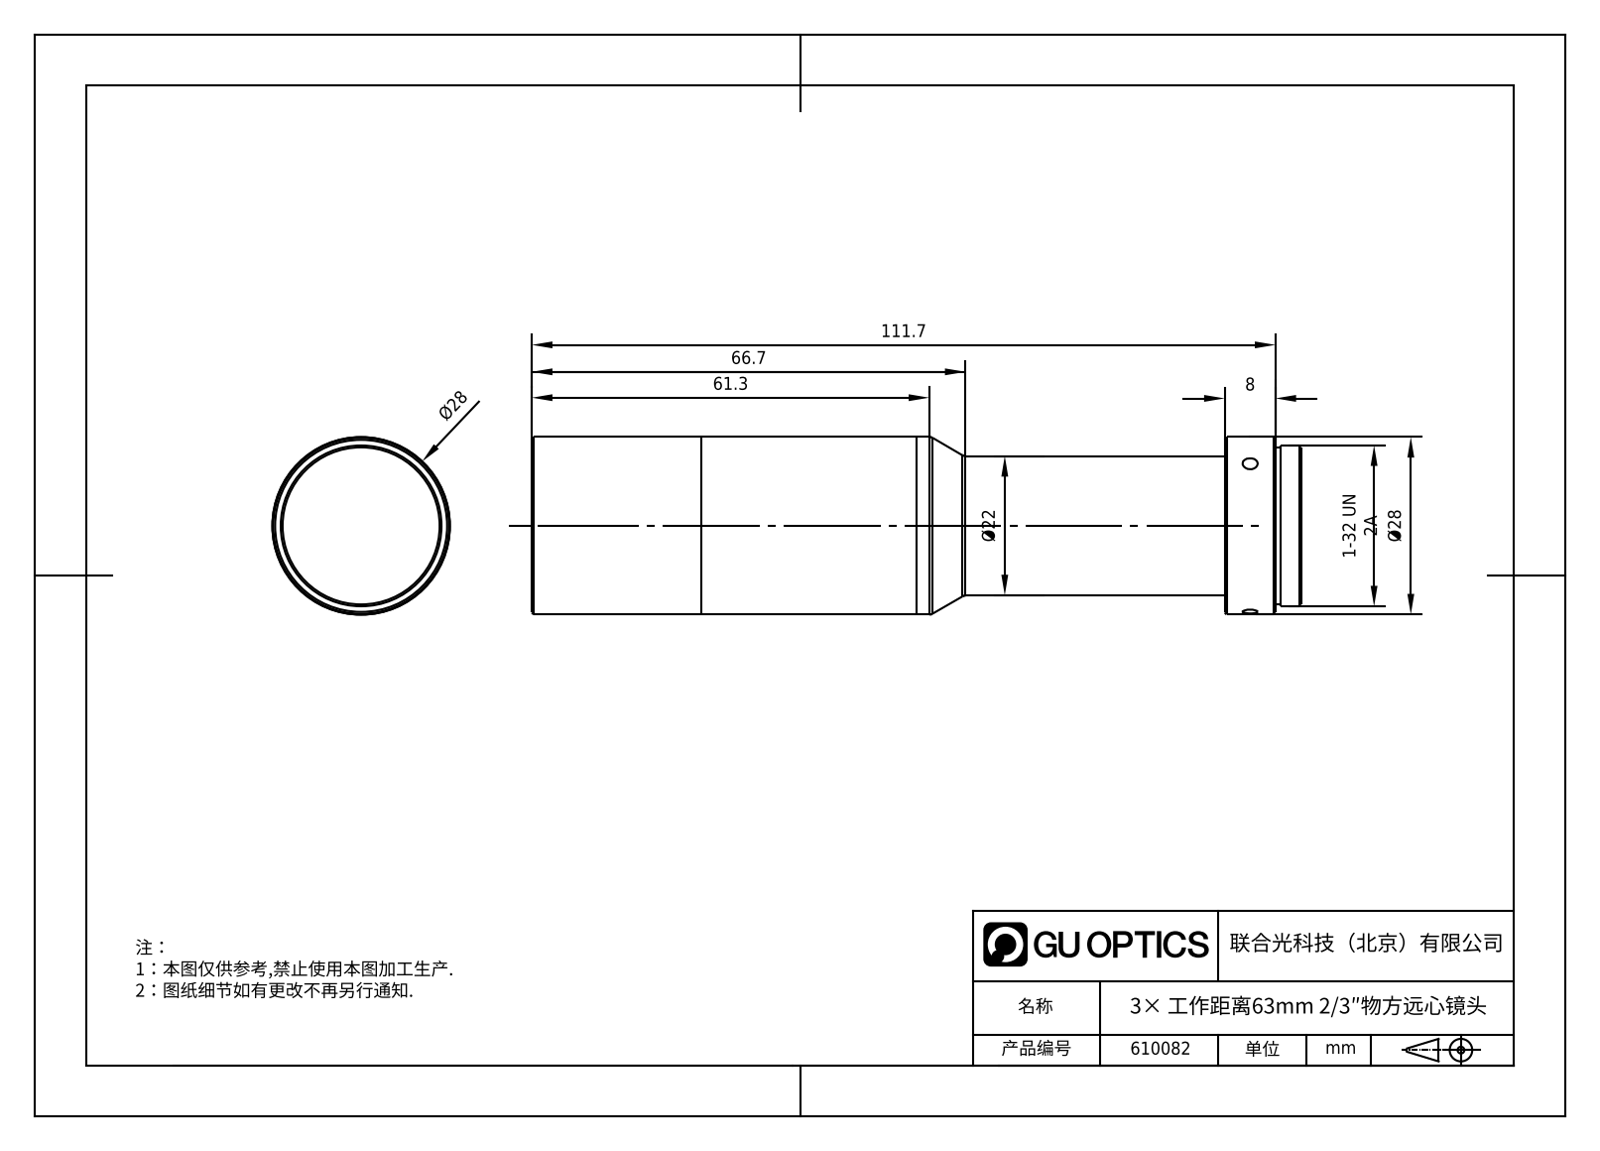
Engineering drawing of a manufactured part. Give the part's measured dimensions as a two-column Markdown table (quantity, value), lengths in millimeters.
| quantity | value |
| --- | --- |
| part name | WWH30-63ATV3 |
| STEP written by | SolidWorks 2017 (CONFIG_CONTROL_DESIGN) |
| units | millimeters |
| bodies | 1 solid, 29 faces (5 planar, 10 cylindrical, 14 other) |
| overall size | 115.7 × 28 × 28 |
| volume | 61 380 mm³ |
| surface area | 10 936 mm² |
| round bosses / shafts (diameter × count) | 28 × 1, 25.4 × 1, 24.4 × 1, 22 × 1 |
| main face-to-face distances | 115.7, 103.7, 12, 111.7, 8, 4, 112.5, 8.8, 0.8, 3.2 |
